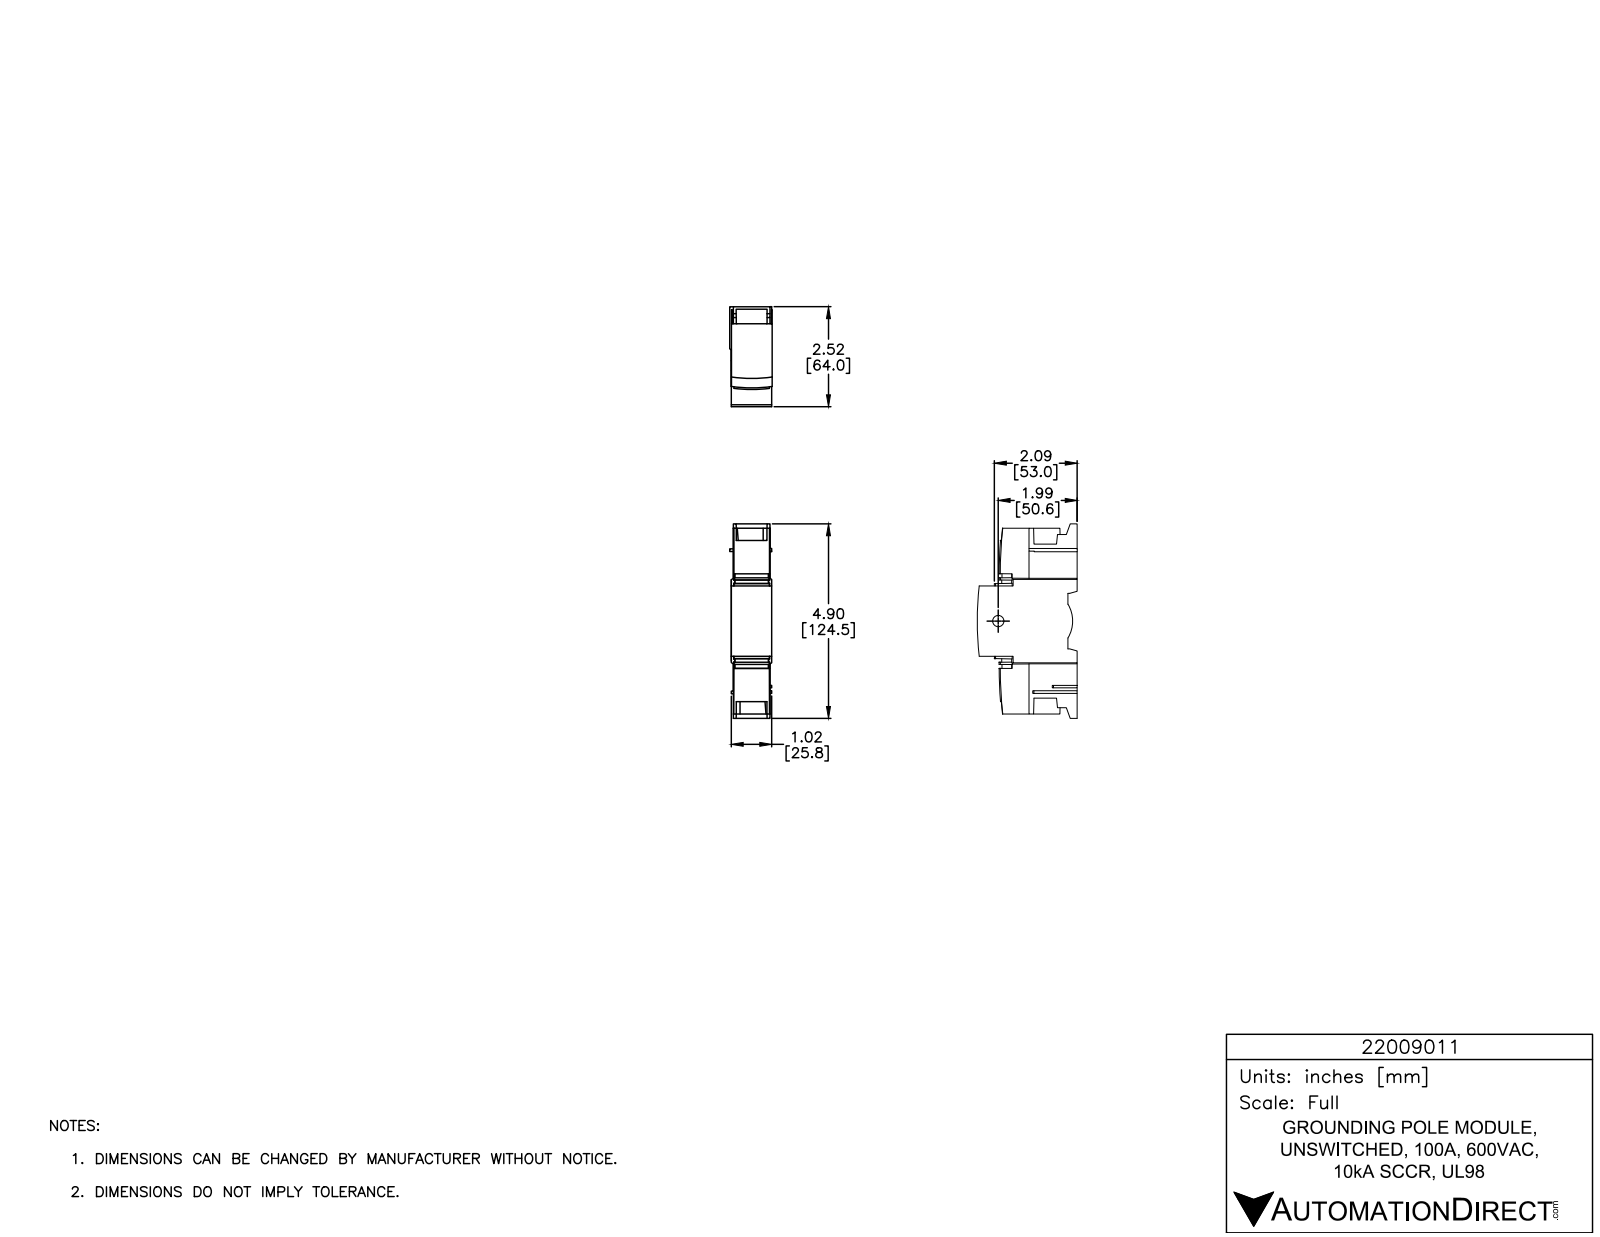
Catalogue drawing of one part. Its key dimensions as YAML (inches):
part_name: "22009011"
step_written_by: "SolidWorks 2015 (AUTOMOTIVE_DESIGN)"
units: inches
bodies: {solids: 1, faces: 166, planar: 151, cylindrical: 11, other: 4}
overall_size: [4.902, 2.519, 1.055]
volume: 7.941
surface_area: 43.37
round_holes:
  - {diameter: 0.283, count: 1}
partial_cylinders:
  - {radius: 0.827, count: 1}
  - {radius: 3.543, count: 1}
  - {radius: 3.646, count: 1}
  - {radius: 7.874, count: 1}
face_to_face_distances: [1.016, 0.051, 0.965, 0.972, 0.921, 0.043, 0.553, 0.169, 0.752, 1.189]
